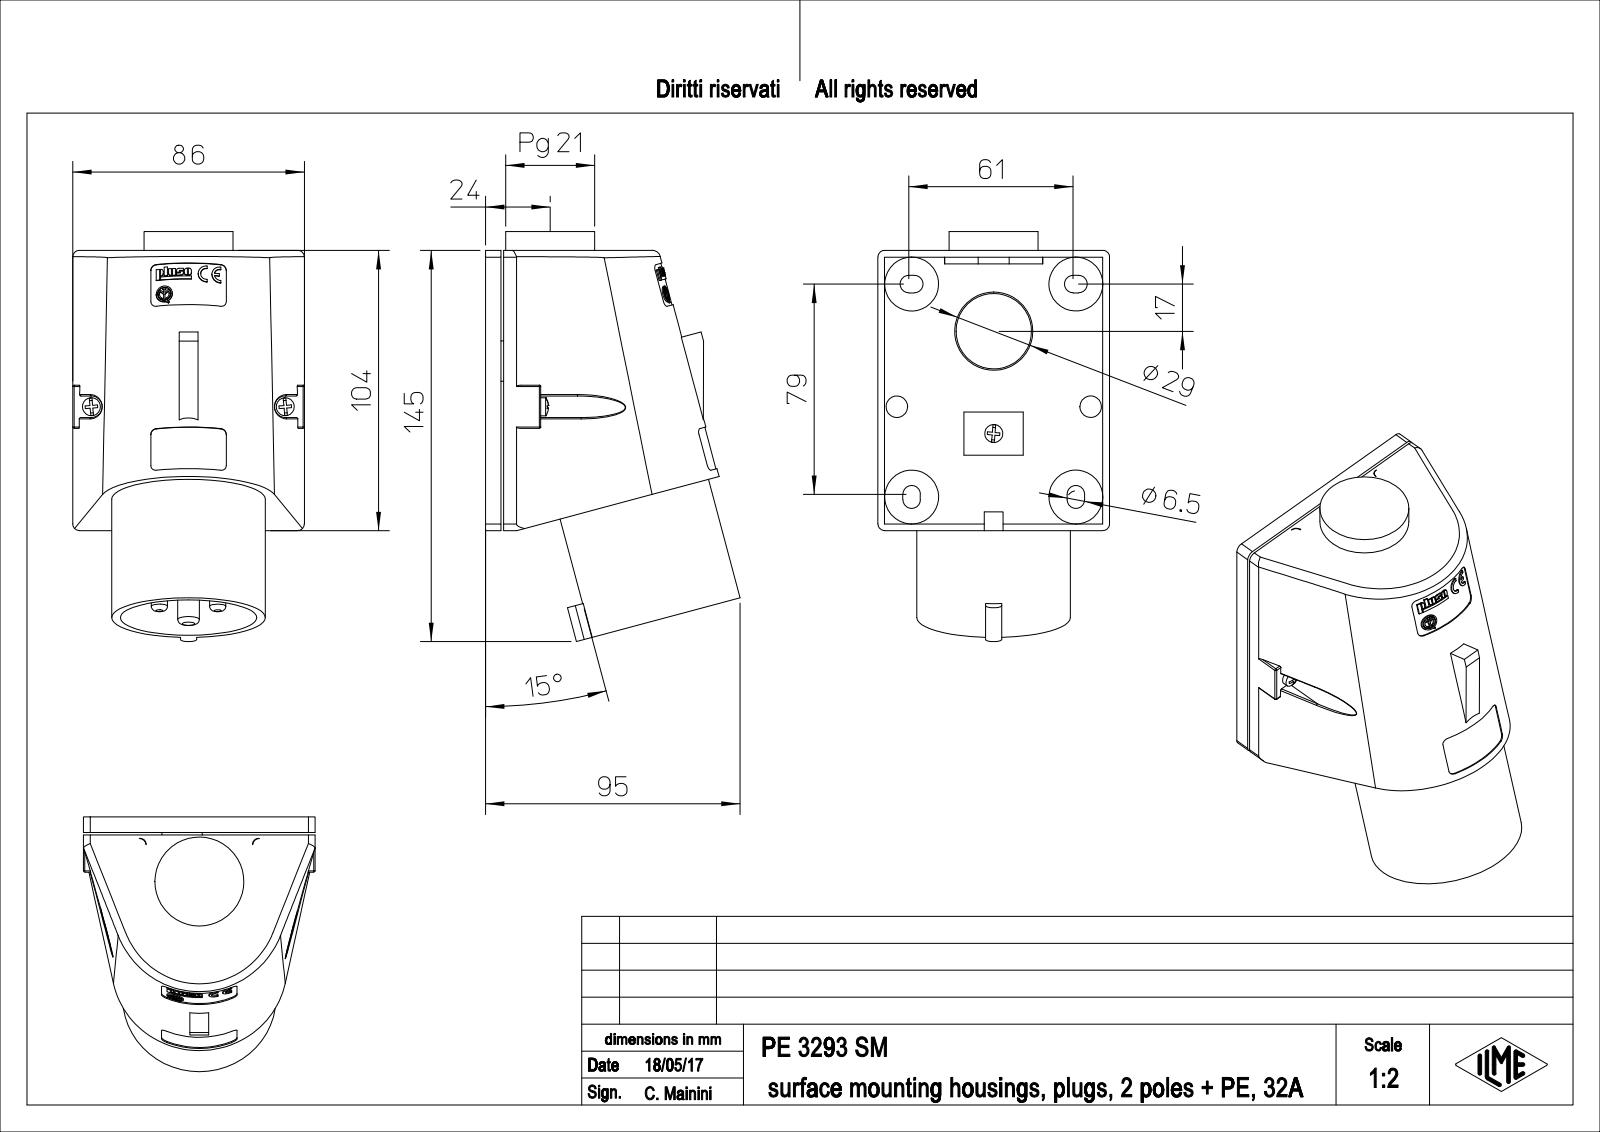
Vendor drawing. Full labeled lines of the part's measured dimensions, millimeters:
Part name (STEP PRODUCT): PE_3293_SM
STEP written by: PTC Creo Elements/Direct Modeling 19.0E 27-Jun-2016 (C) Parametric Technology GmbH (AUTOMOTIVE_DESIGN)
Units: millimetres
Bodies: 1 solid, 1004 faces (657 planar, 213 cylindrical, 134 other)
Overall size (bounding box): 152.14 × 94.53 × 86
Volume: 491 313 mm³ · Surface area: 90 882 mm²
Round holes (diameter × count): ⌀2.8 ×2, ⌀3.2 ×2, ⌀4 ×2, ⌀4.5 ×2, ⌀6.1 ×2, ⌀4.2 ×1, ⌀5.04 ×1, ⌀27.54 ×1, ⌀29 ×1, ⌀32 ×1, ⌀50.6 ×1
Round bosses / shafts (diameter × count): ⌀6.7 ×5, ⌀20 ×4, ⌀8 ×3, ⌀6 ×3, ⌀3 ×2, ⌀57 ×1, ⌀50 ×1, ⌀33 ×1
Partial cylindrical surfaces — rounded edges, fillets, slot ends (radius × count): R0.5 ×22, R0.17 ×11, R2 ×10, R0.86 ×9, R3.25 ×8, R2.5 ×6, R0.3 ×4, R4.5 ×4
Main face-to-face distances: 0.98, 4.75, 5.73, 1, 7, 5.75, 6.73, 2.25, 2.5, 8
Hole centre spacings: 12.51, 21, 37.36, 45.61, 72, 11.94, 21.66, 23.48
